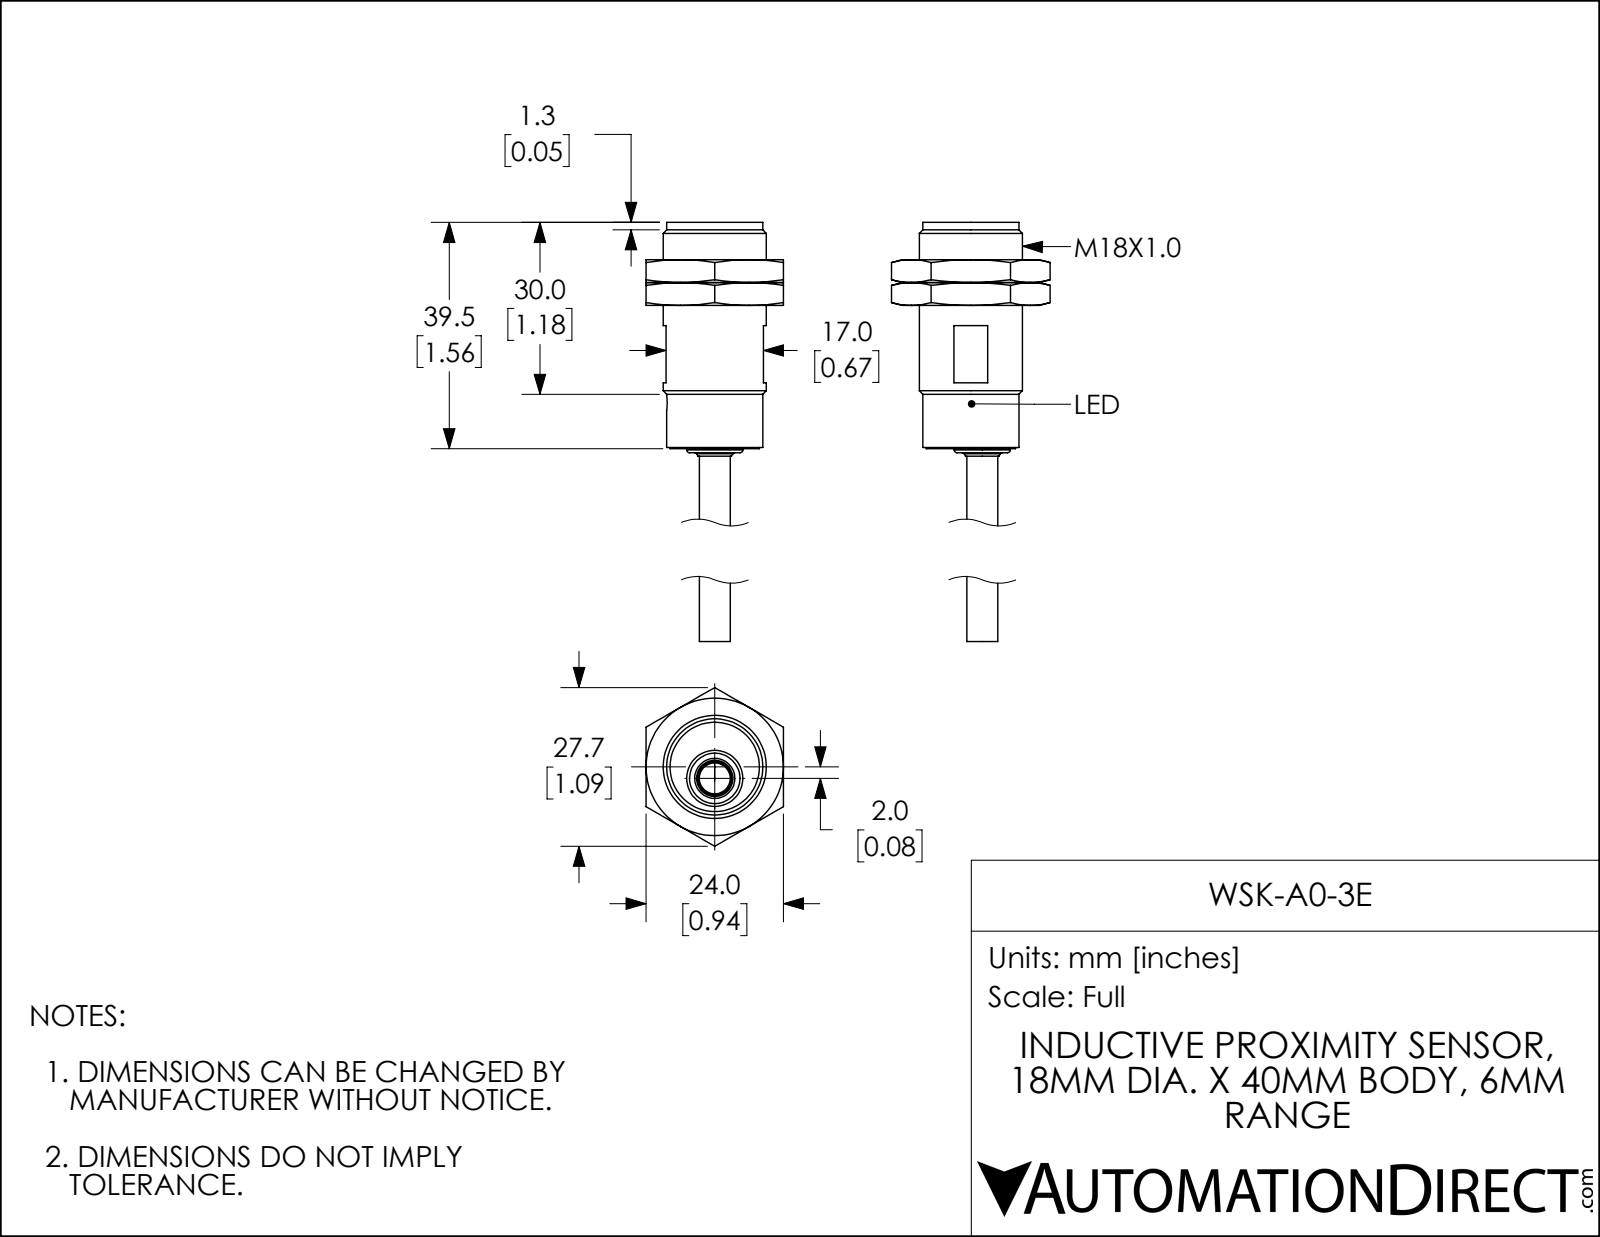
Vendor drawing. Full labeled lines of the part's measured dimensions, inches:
Part name (STEP PRODUCT): WSK-A0-3E-M18x1; WSK-A0-3E-BODY; WSK-A0-3E
STEP written by: SolidWorks 2017 (AUTOMOTIVE_DESIGN)
Units: inches
Bodies: 3 solids, 91 faces (31 planar, 18 cylindrical, 42 other)
Overall size (bounding box): 3.13 × 1.091 × 0.945
Volume: 0.776 in³ · Surface area: 8.398 in²
Round holes (diameter × count): ⌀0.098 ×1, ⌀0.666 ×1
Round bosses / shafts (diameter × count): ⌀0.709 ×1, ⌀0.661 ×1, ⌀0.614 ×1, ⌀0.386 ×1, ⌀0.213 ×1
Main face-to-face distances: 0.157, 0.945, 0.413, 0.256, 0.315, 0.571, 0.138, 0.807, 1.555, 0.984
